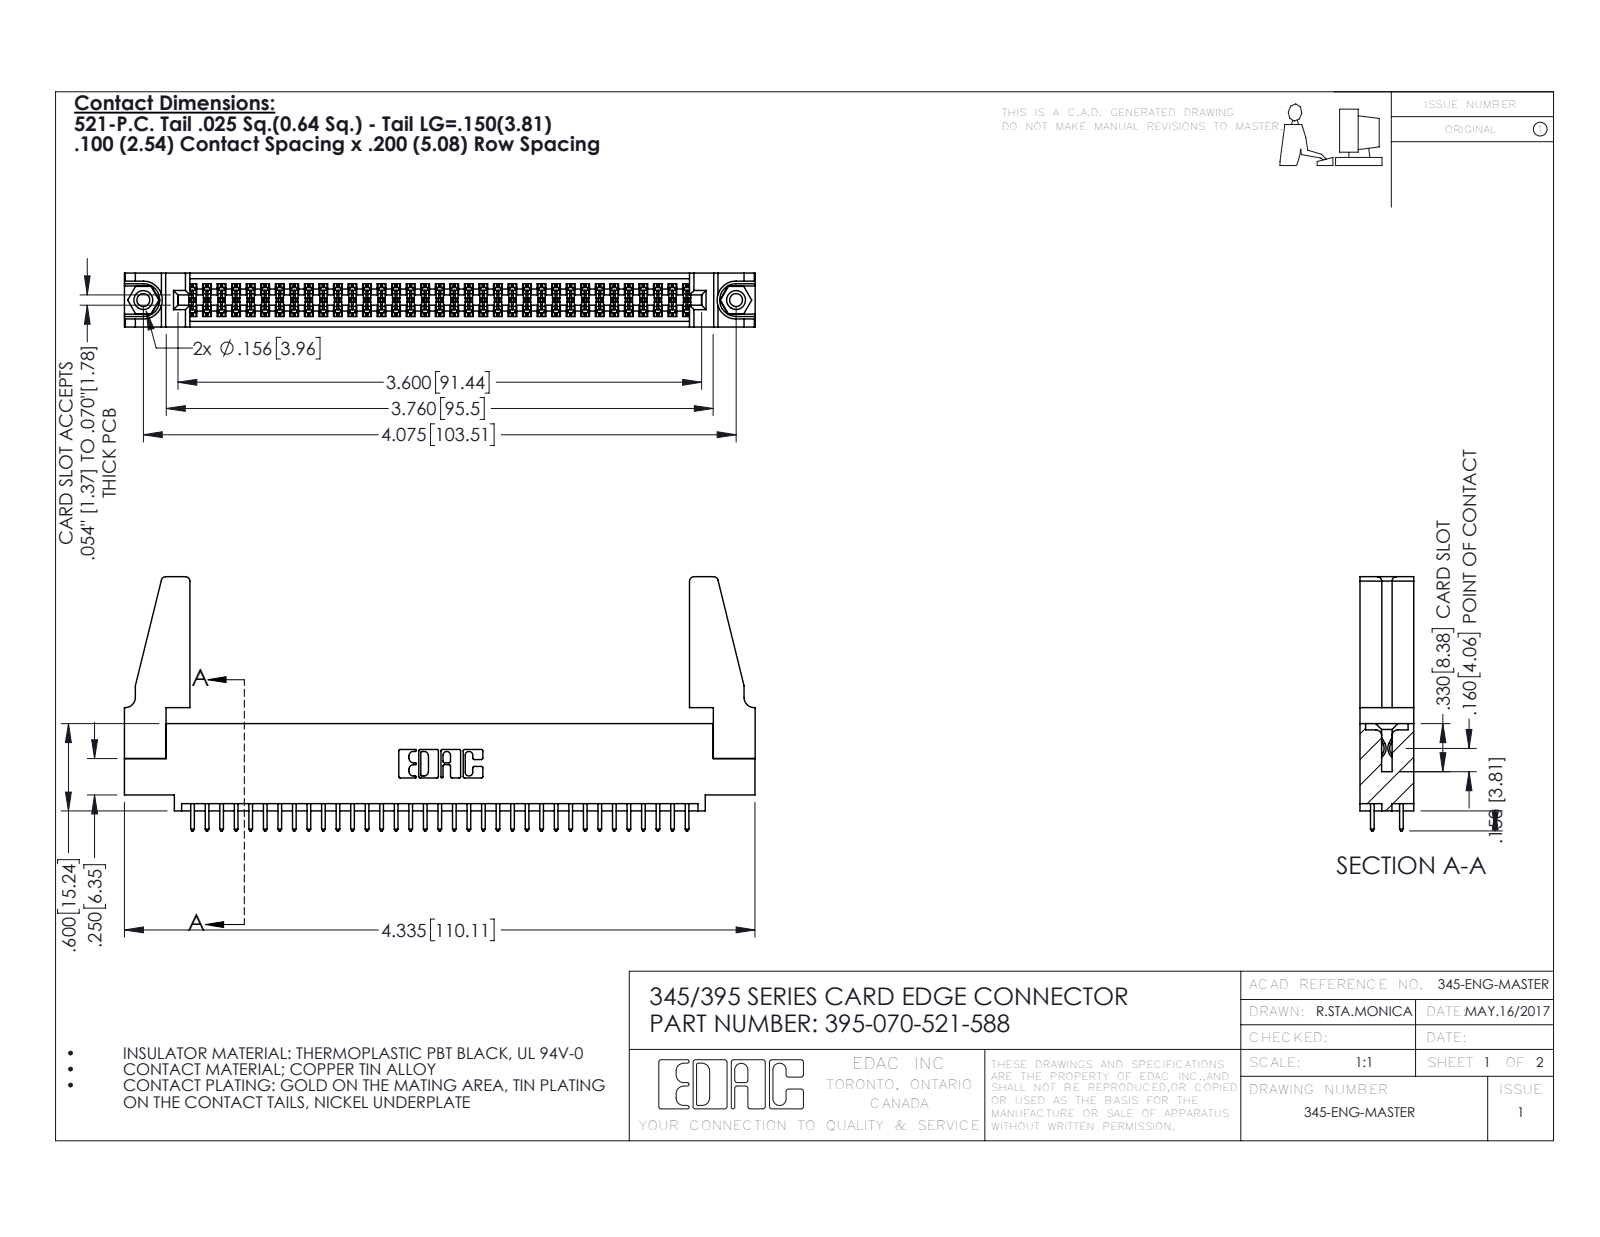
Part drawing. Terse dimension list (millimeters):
name: 345-250-001_345-250-001-102; 345 Part_0.110 Offset - 0.156 Dia-TH; 395-070-521-588; 345-220-078_345-220-088 (+1 more)
written by: SolidWorks 2016 (CONFIG_CONTROL_DESIGN)
unit: mm
bodies: 75 solids, 3754 faces (2466 planar, 1272 cylindrical, 16 other)
size: 110.1 × 44.4 × 9.4
volume: 13 800 mm³; area: 18 460 mm²
holes: 2× ⌀2.3, 2× ⌀3.2, 2× ⌀4, 1× ⌀1.6
bosses: 2× ⌀3.9
rounds: 105× R0.2, 70× R0.3, 22× R0.3, 8× R0.8, 6× R0.2, 6× R0.8, 3× R0.7, 2× R0.4
face distances: 1.8, 7.6, 9.4, 5.1, 2.5, 6.9, 0.6, 5.7, 4.4, 3.8
hole spacings: 6.9, 97.5, 103.5
